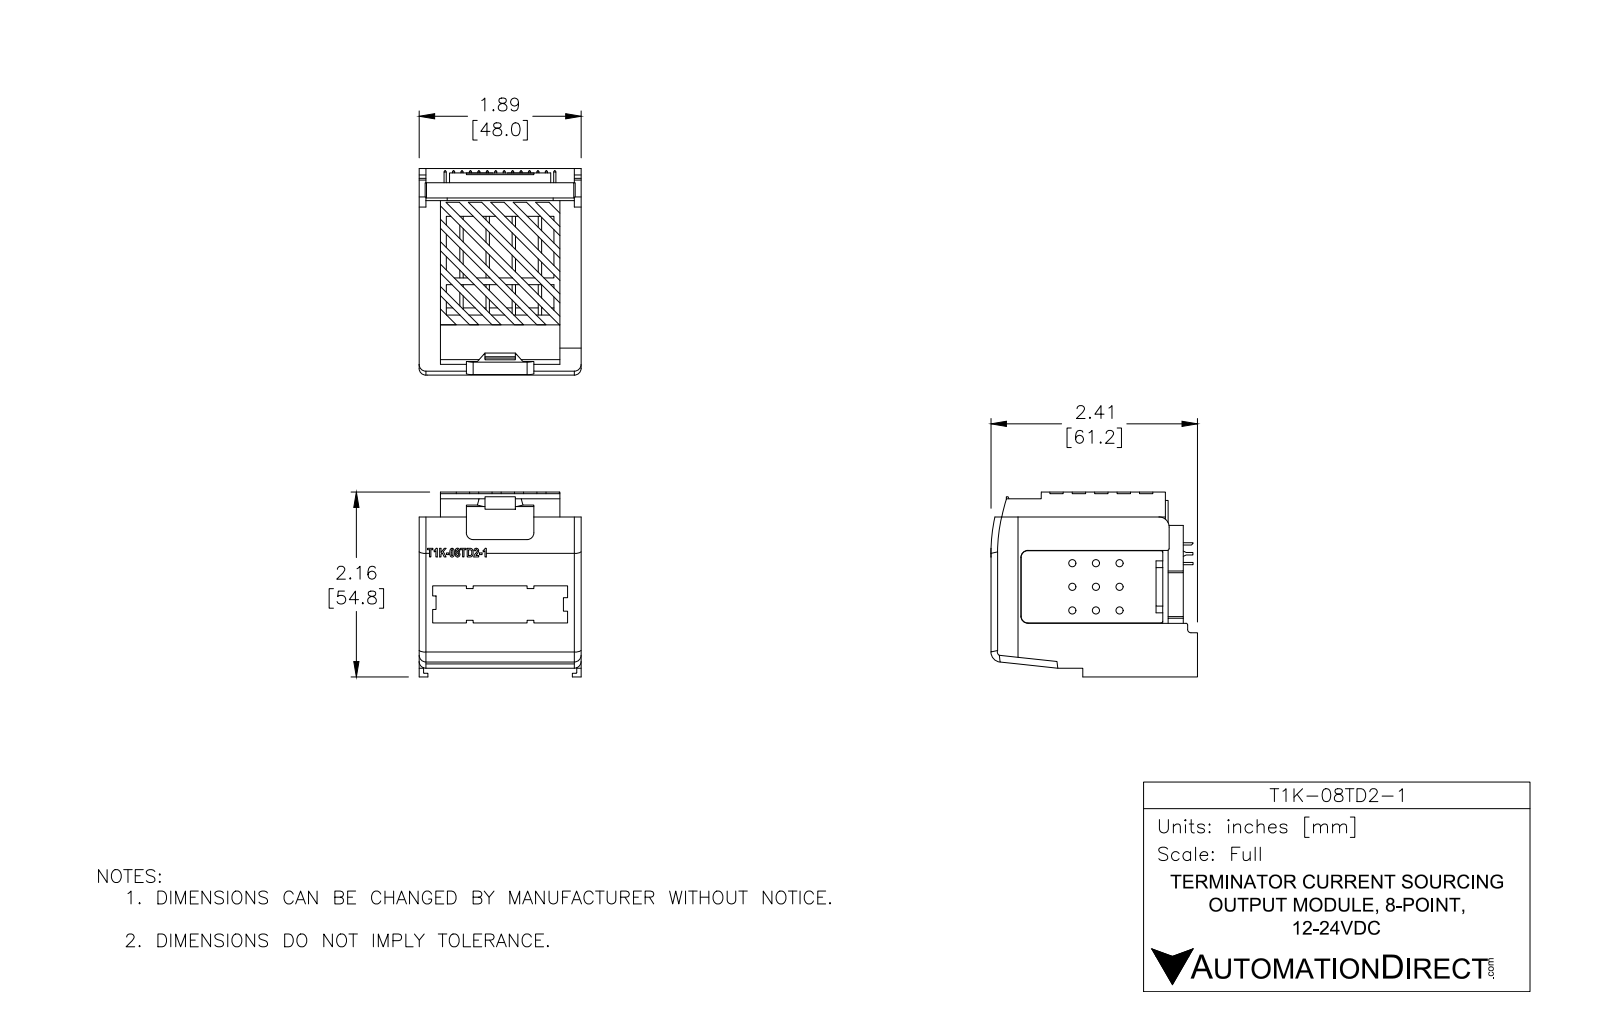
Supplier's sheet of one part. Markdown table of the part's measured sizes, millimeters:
| quantity | value |
| --- | --- |
| part name | T1K-08TD2-1 |
| STEP written by | SolidWorks 2013 (AUTOMOTIVE_DESIGN) |
| units | millimeters |
| bodies | 1 solid, 568 faces (428 planar, 101 cylindrical, 39 other) |
| overall size | 65.1 × 61.36 × 47.6 |
| volume | 30 279 mm³ |
| surface area | 35 941 mm² |
| round holes (diameter × count) | 3 × 8 |
| round bosses / shafts (diameter × count) | 0.7 × 28 |
| partial cylindrical surfaces (radius × count) | 3.5 × 10, 1 × 5, 0.25 × 3, 0.55 × 3, 1.5 × 2, 8 × 1, 10 × 1, 18 × 1 |
| main face-to-face distances | 2, 45.6, 47.6, 43.6, 55.35, 49.9, 6.55, 39.05, 59.8, 9.9 |
| hole center spacings | 5.2, 10.4, 15.6, 20.8, 26, 31.2, 36.4 |
